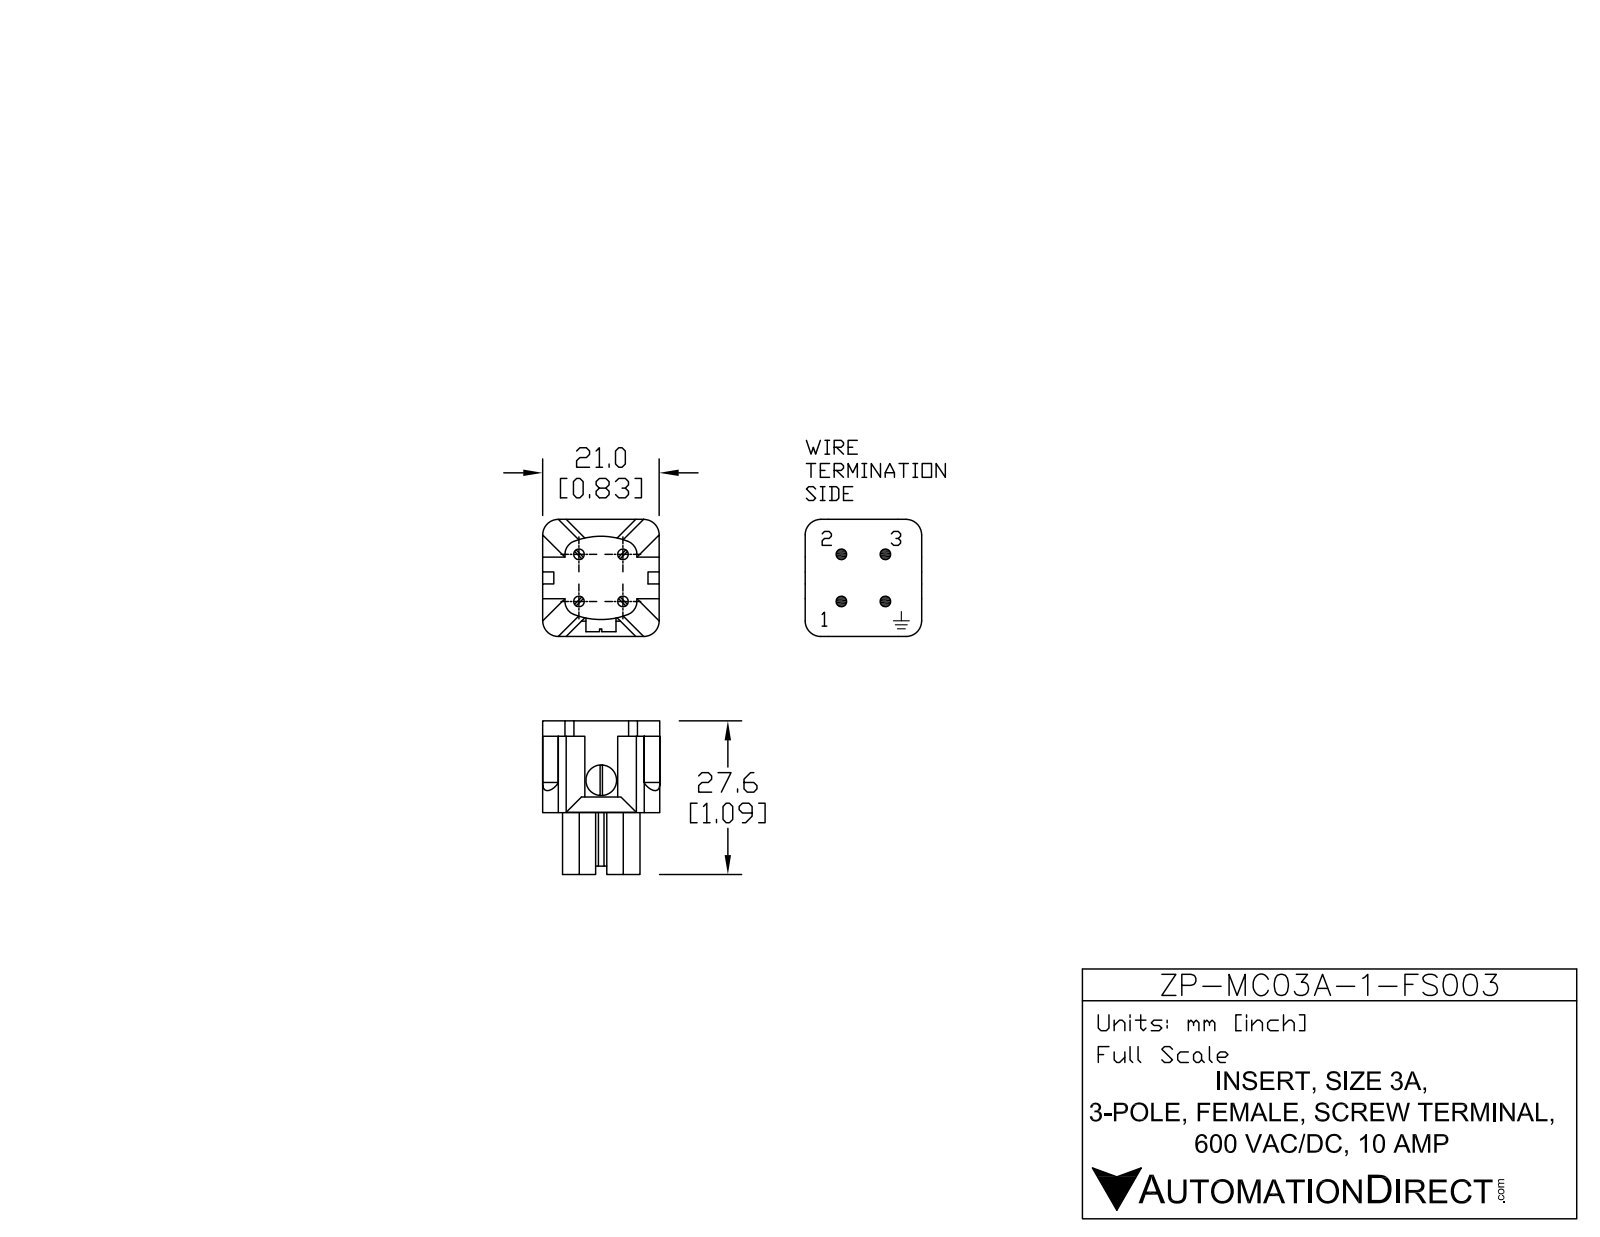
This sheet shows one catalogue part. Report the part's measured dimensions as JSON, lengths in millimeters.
{"part_name": "ZP-3A-3-FS-INSERT", "step_written_by": "SolidWorks 2011 (AUTOMOTIVE_DESIGN)", "units": "millimeters", "bodies": {"solids": 1, "faces": 114, "planar": 81, "cylindrical": 33, "other": 0}, "overall_size": [27.55, 21, 21], "volume_mm3": 7023, "surface_area_mm2": 3388, "round_holes": [[1.9, 7], [3.5, 1]], "round_bosses_or_shafts": [[5.5, 1]], "partial_cylinders_radius": [[3, 8], [2.5, 4], [2.8, 4], [0.5, 2], [2.06, 2], [13.65, 2]], "face_to_face_distances": [3.55, 17.45, 21, 16.45, 1, 4.94, 13.9, 3.94, 27.55, 11.1], "hole_center_spacings": [8, 8.22, 11.47, 8.44, 11.31, 11.63]}
